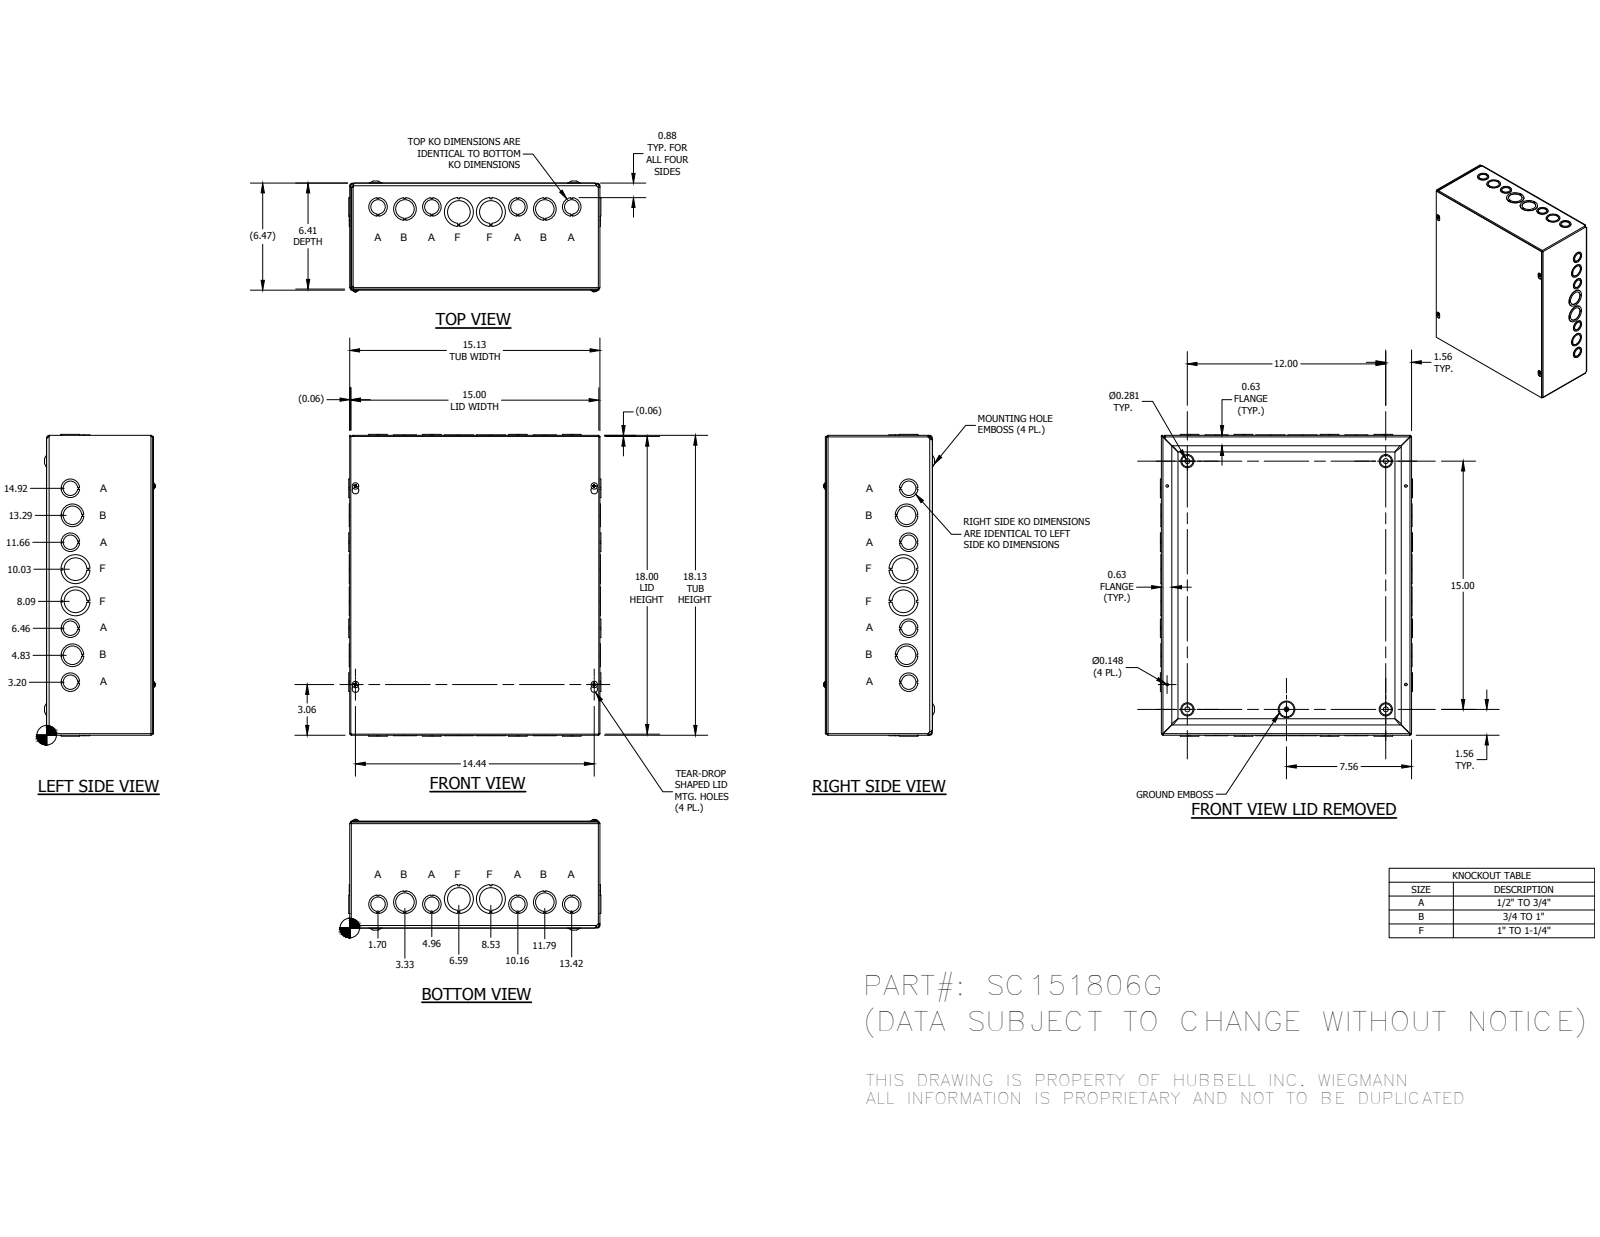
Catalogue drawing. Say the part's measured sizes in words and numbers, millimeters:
The part is named "SC1518GBKP; SC151806GWRA; SC1518GLID; 34056 (+1 more)". Its 3-D file was written by "Autodesk Inventor 2014 (CONFIG_CONTROL_DESIGN)". It is 38 solids with 1254 faces: 838 planar, 265 cylindrical and 151 other. Overall it measures 463.52 by 387.32 by 170 millimeters. Round holes: 12 of diameter 28.57, 8 of diameter 22.22, 8 of diameter 34.92, 4 of diameter 3.76, 4 of diameter 7.62, 4 of diameter 44.45, 1 of diameter 4.19. Round bosses or shafts: 4 of diameter 9.75, 4 of diameter 4.17, 1 of diameter 5.8. Partial cylindrical surfaces (rounded edges, fillets, slot ends): 8 of radius 0.79, 8 of radius 2.37, 4 of radius 1.4, 4 of radius 1.57, 4 of radius 2.38, 4 of radius 2.79, 4 of radius 2.97, 4 of radius 3.15. The main face-to-face distances are 1.57, 161.12, 162.69, 1.59, 162.71, 164.28, 1.58, 384.18, 382.6, 382.61. The hole center spacings are 41.52, 42.15, 49.09, 82.94, 91.03, 132.17, 173.51, 214.88.
